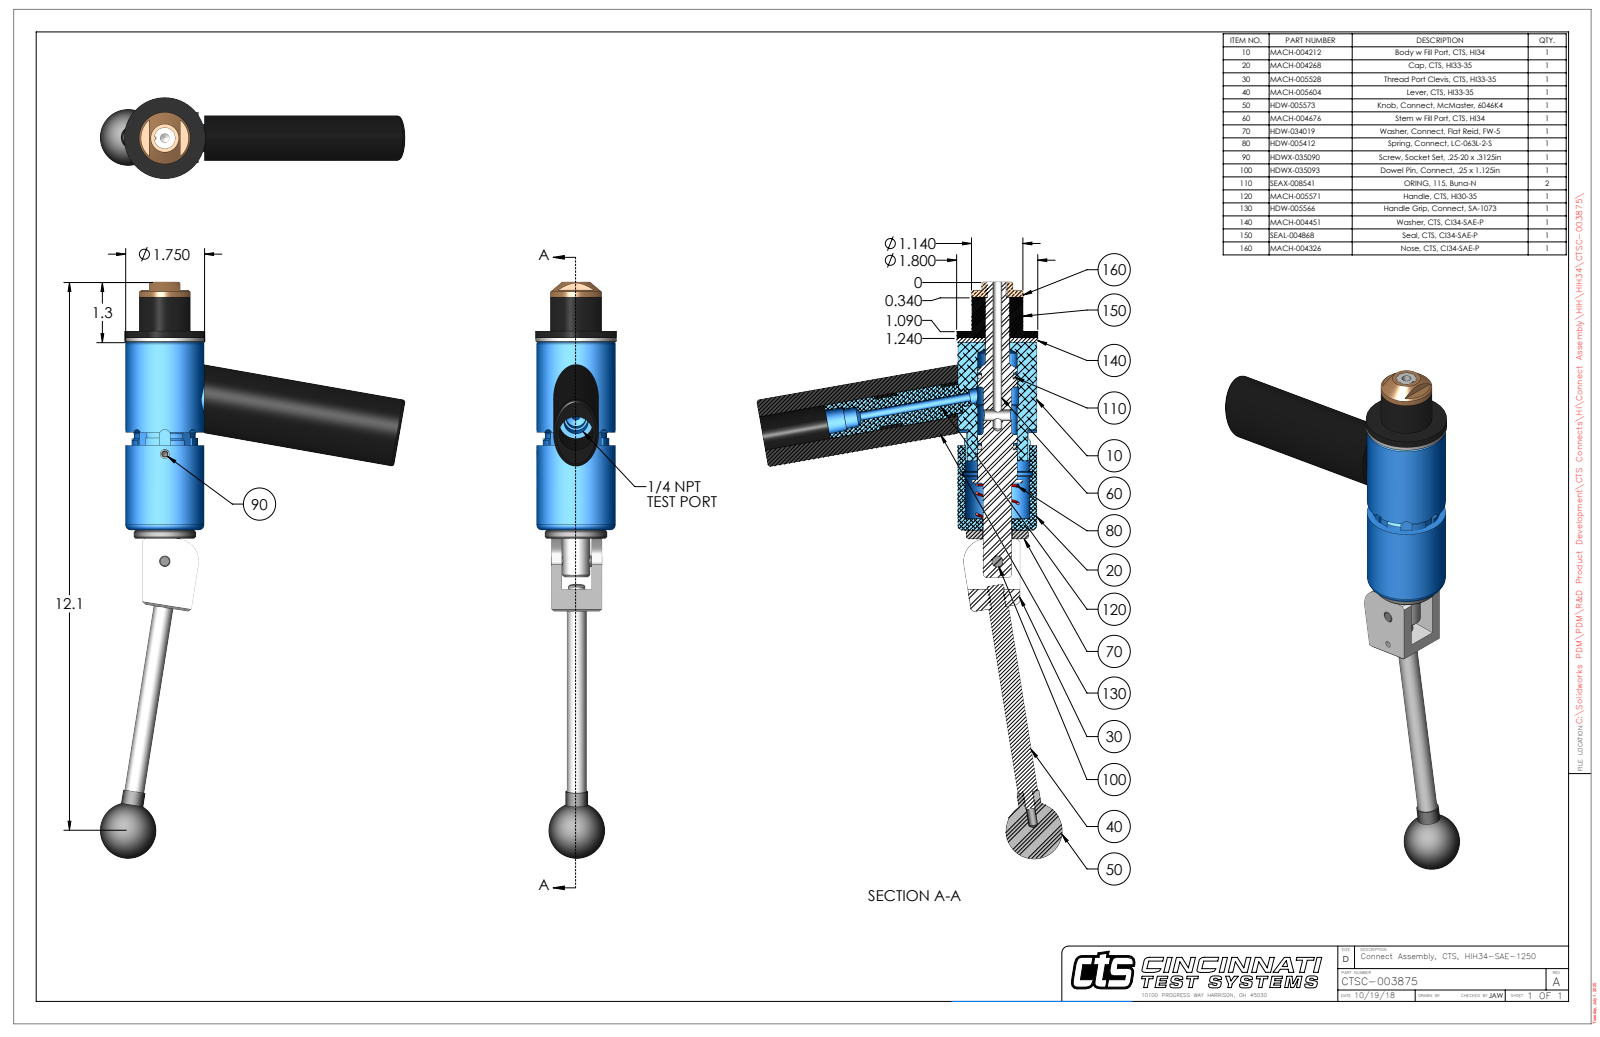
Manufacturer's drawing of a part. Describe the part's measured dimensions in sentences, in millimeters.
The part is named "CTSC-003875". Its 3-D file was written by "SolidWorks 2023 (AUTOMOTIVE_DESIGN)". It is 10 solids with 341 faces: 123 planar, 143 cylindrical and 75 other. Overall it measures 324.4 by 171.8 by 45.7 millimeters. Its volume is 309 700 cubic millimeters and its surface area 78 390 square millimeters. Round holes: 2 of diameter 5.1, 1 of diameter 3.8, 1 of diameter 4.7, 1 of diameter 5.2, 1 of diameter 6.3, 1 of diameter 6.4, 1 of diameter 6.4, 1 of diameter 8, 1 of diameter 10.7, 1 of diameter 11.1, 1 of diameter 13.5, 1 of diameter 13.7. Round bosses or shafts: 2 of diameter 12.7, 2 of diameter 11.2, 2 of diameter 6.4, 1 of diameter 45.7, 1 of diameter 44.5, 1 of diameter 35.1, 1 of diameter 29, 1 of diameter 19.1. Partial cylindrical surfaces (rounded edges, fillets, slot ends): 4 of radius 3.2, 2 of radius 0.7, 1 of radius 4.2, 1 of radius 4.2, 1 of radius 4.7, 1 of radius 8.4, 1 of radius 12.7, 1 of radius 17.7. The main face-to-face distances are 2.4, 108.2, 105.8, 22.9, 25.2, 131, 28.4, 19.1, 3.8, 6.2. The hole center spacings are 18.8, 60.4, 79.1.
